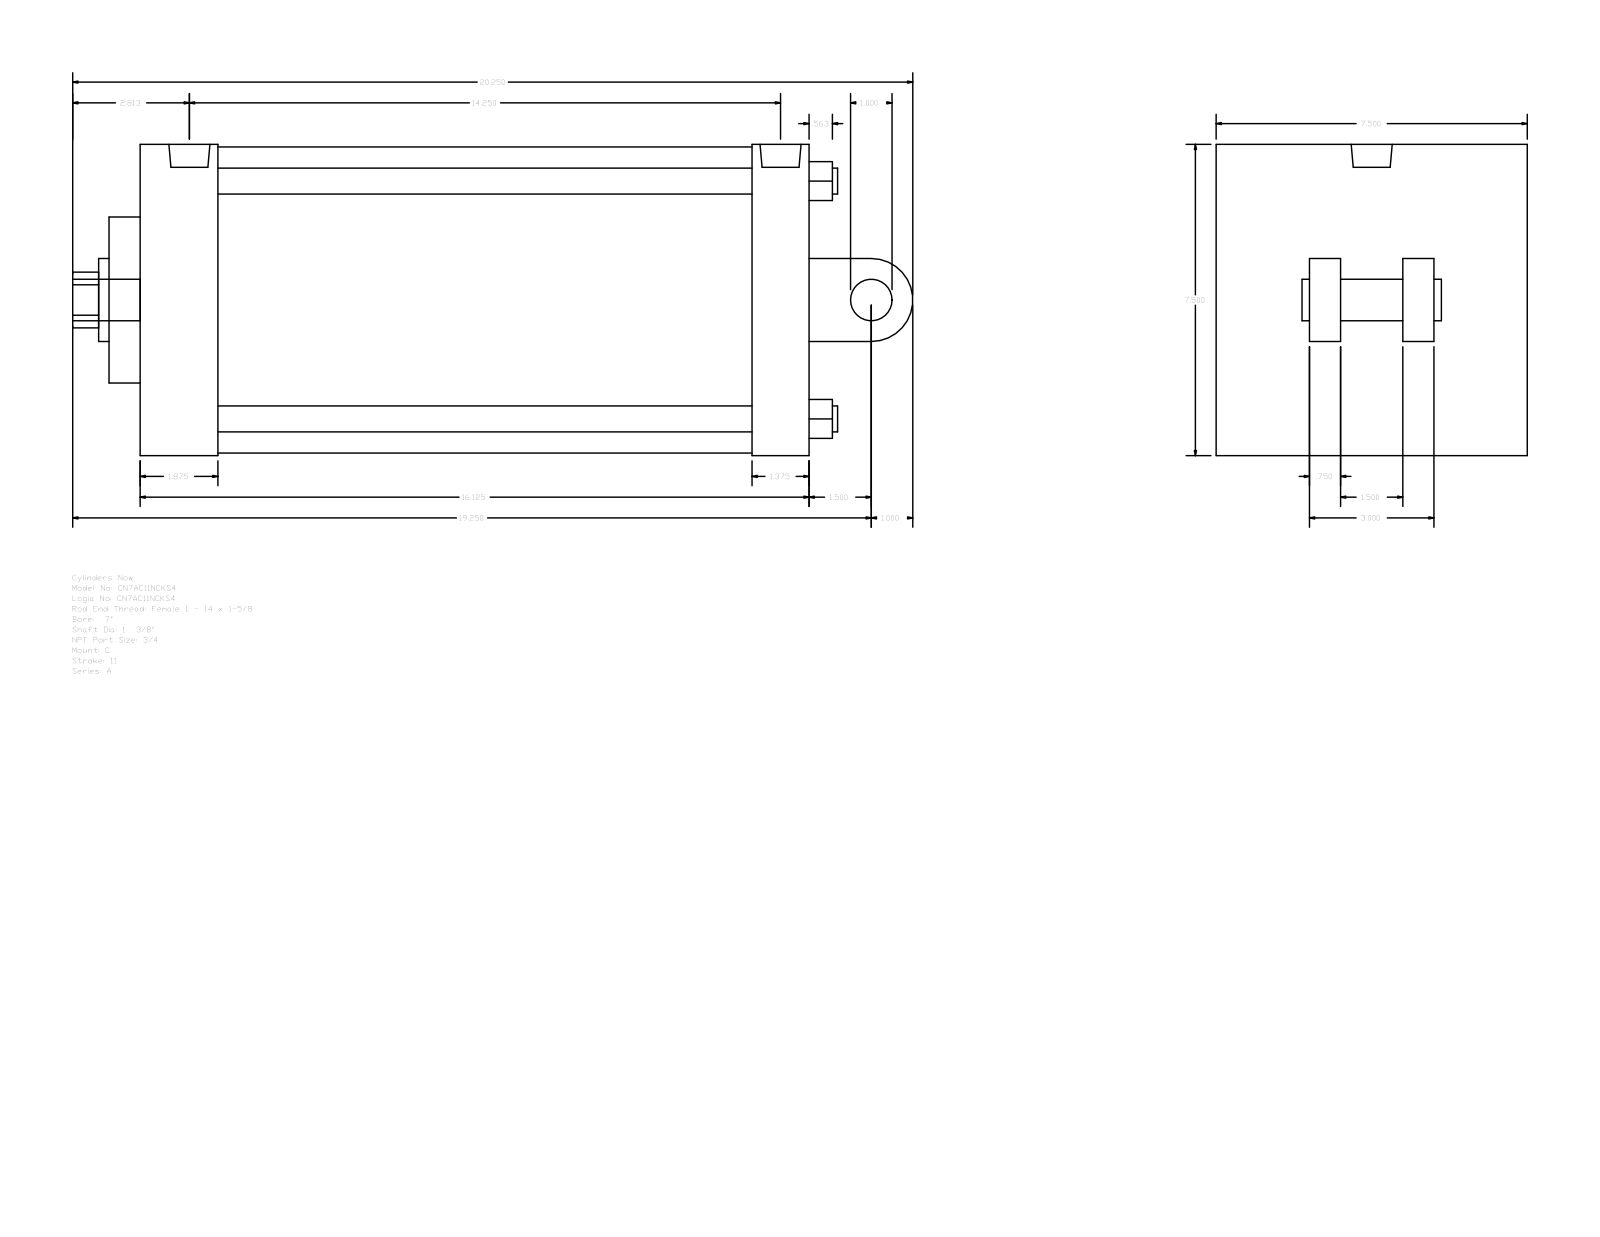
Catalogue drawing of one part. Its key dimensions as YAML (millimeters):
part_name: "A_C__0700_1.375"
step_written_by: "GSSL Pune (CONFIG_CONTROL_DESIGN)"
units: millimeters
bodies: {solids: 0, faces: 104, planar: 75, cylindrical: 29, other: 0}
overall_size: [514.35, 190.5, 190.5]
round_holes:
  - {diameter: 15.88, count: 4}
  - {diameter: 15.08, count: 2}
  - {diameter: 25.12, count: 1}
  - {diameter: 34.92, count: 1}
  - {diameter: 50.8, count: 1}
  - {diameter: 187.32, count: 1}
round_bosses_or_shafts:
  - {diameter: 25.4, count: 2}
  - {diameter: 15.08, count: 2}
  - {diameter: 25.12, count: 1}
partial_cylinders:
  - {radius: 17.06, count: 1}
  - {radius: 25.4, count: 1}
face_to_face_distances: [190.5, 409.58, 76.2, 57.15, 19.04, 428.62, 66.67, 47.63, 361.95, 393.7]
hole_center_spacings: [102.91, 145.54, 205.82, 5.56]
